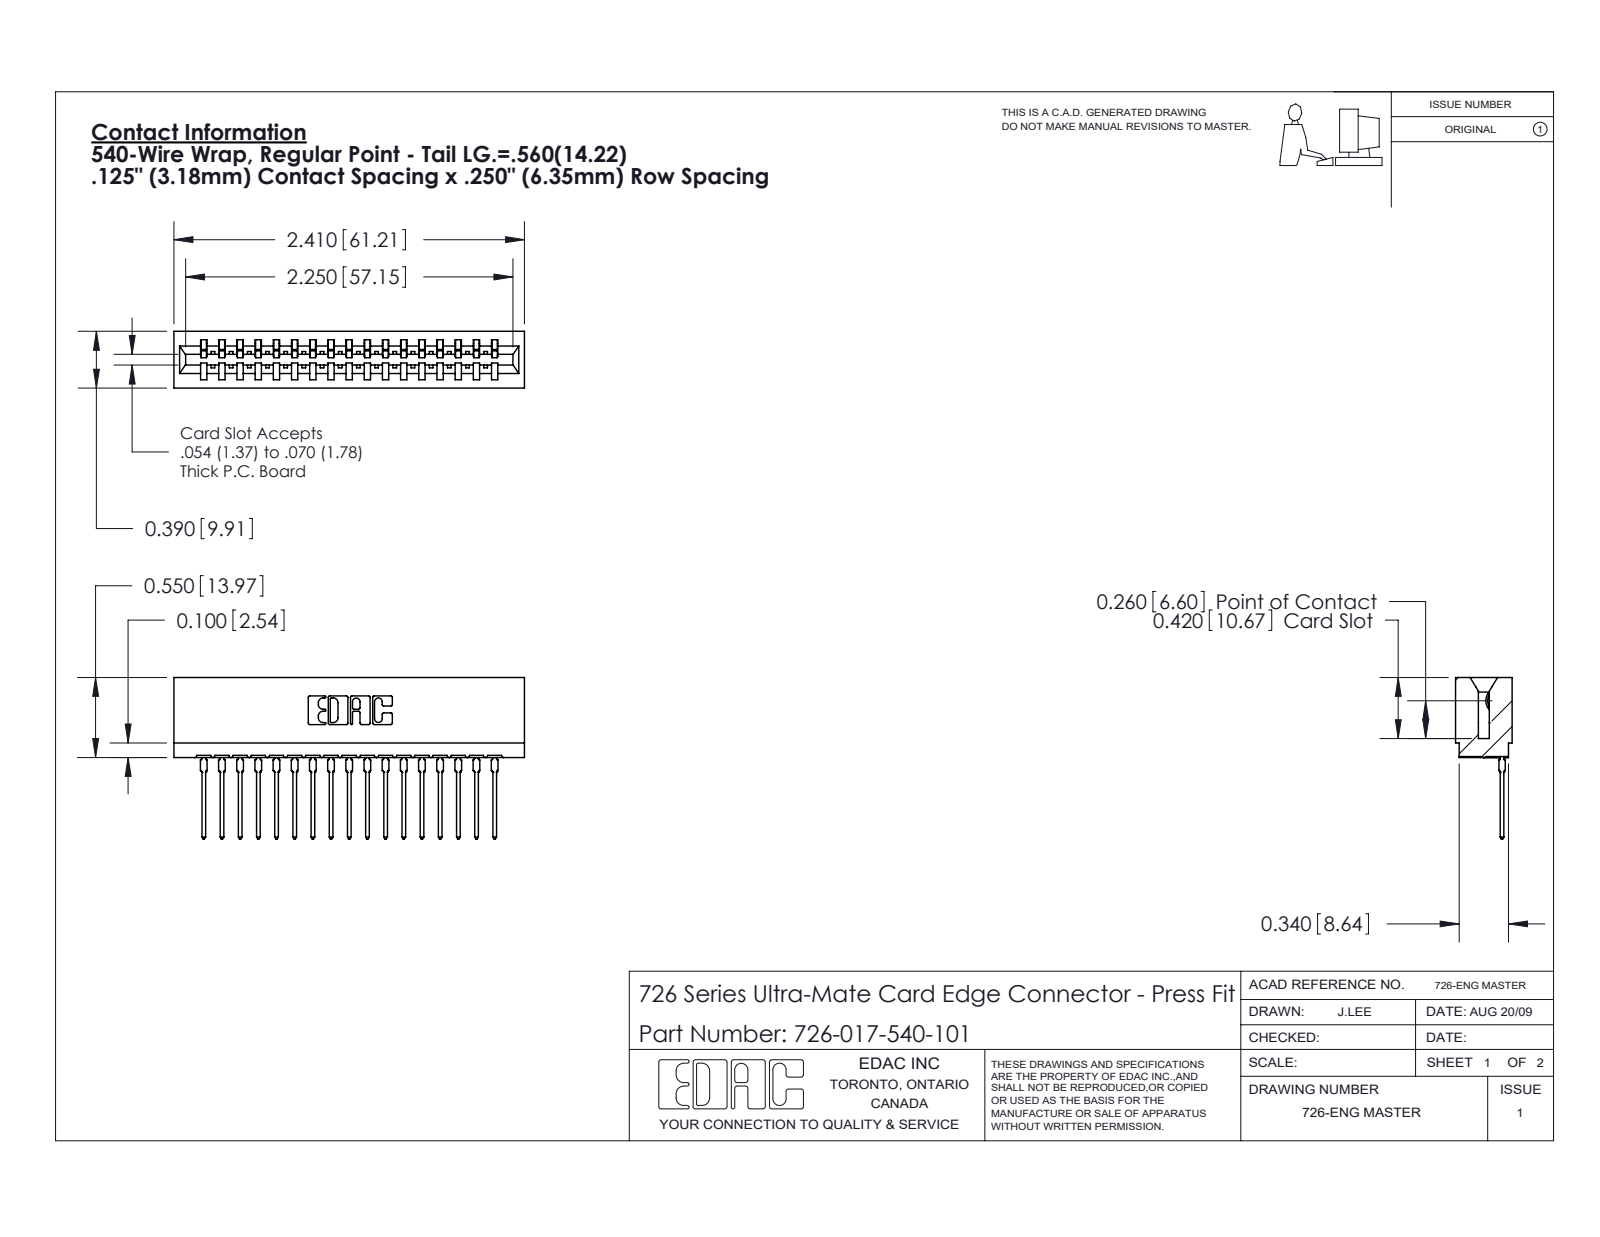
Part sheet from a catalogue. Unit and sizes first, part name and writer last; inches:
Units: inches
Overall size (bounding box): 2.41 × 1.109 × 0.39
Partial cylindrical surfaces — rounded edges, fillets, slot ends (radius × count): R0.021 ×34, R0.01 ×22, R0.015 ×18, R0.007 ×6, R0.031 ×6, R0.005 ×4, R0.011 ×4, R0.026 ×3
Main face-to-face distances: 0.057, 0.333, 0.25, 0.39, 0.025, 0.307, 0.5, 0.083, 0.75, 0.125
Volume: 0.345 in³ · Surface area: 13.11 in²
Bodies: 18 solids, 1933 faces (1126 planar, 365 cylindrical, 442 other)
Part name (STEP PRODUCT): 726-017-540-101; 726 Part_.515 Slot Depth - 01; 746-292-001_540
STEP written by: SolidWorks 2020 (CONFIG_CONTROL_DESIGN)
